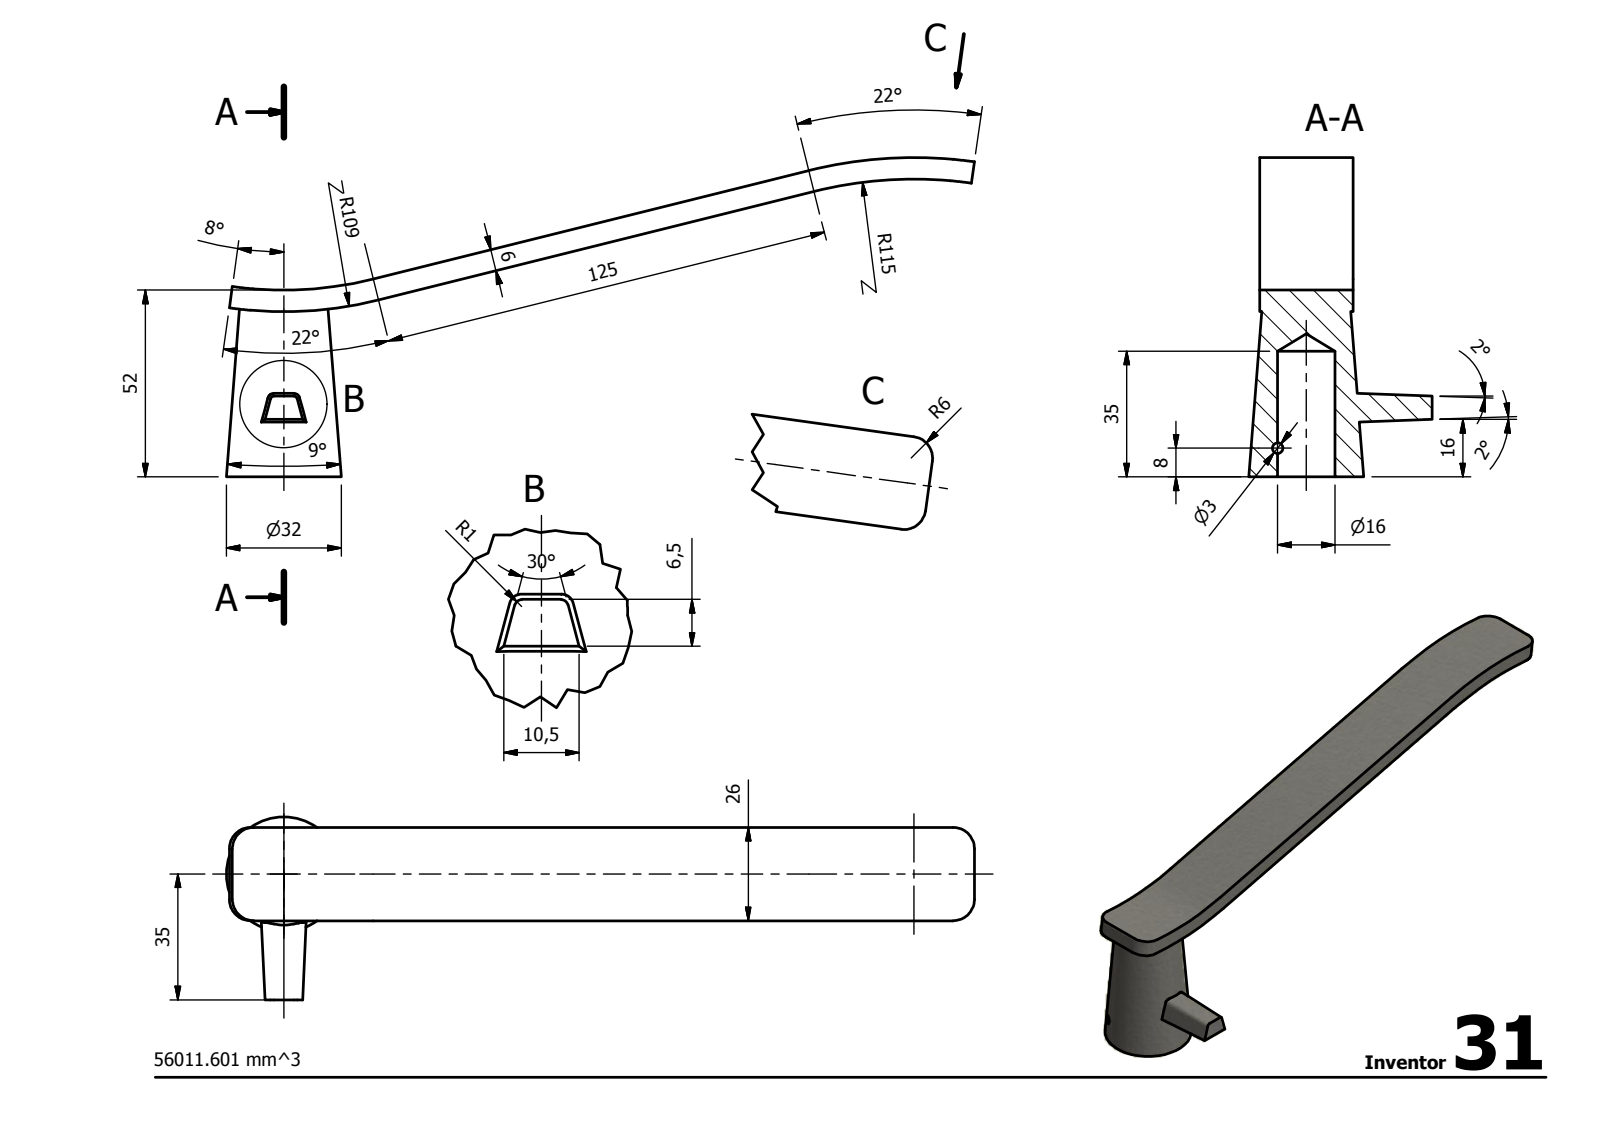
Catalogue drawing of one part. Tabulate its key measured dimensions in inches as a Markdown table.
| quantity | value |
| --- | --- |
| STEP written by | Autodesk Inventor 2014 (AUTOMOTIVE_DESIGN) |
| units | inches |
| bodies | 1 solid, 26 faces (12 planar, 10 cylindrical, 4 other) |
| overall size | 8.202 × 3.5 × 2.008 |
| volume | 3.416 in³ |
| surface area | 32.24 in² |
| round holes (diameter × count) | 0.118 × 1, 0.63 × 1 |
| partial cylindrical surfaces (radius × count) | 0.236 × 4, 4.055 × 1, 4.291 × 1, 4.528 × 1, 4.764 × 1 |
| main face-to-face distances | 0.235, 1.024, 7.864, 1.89, 0.866 |
